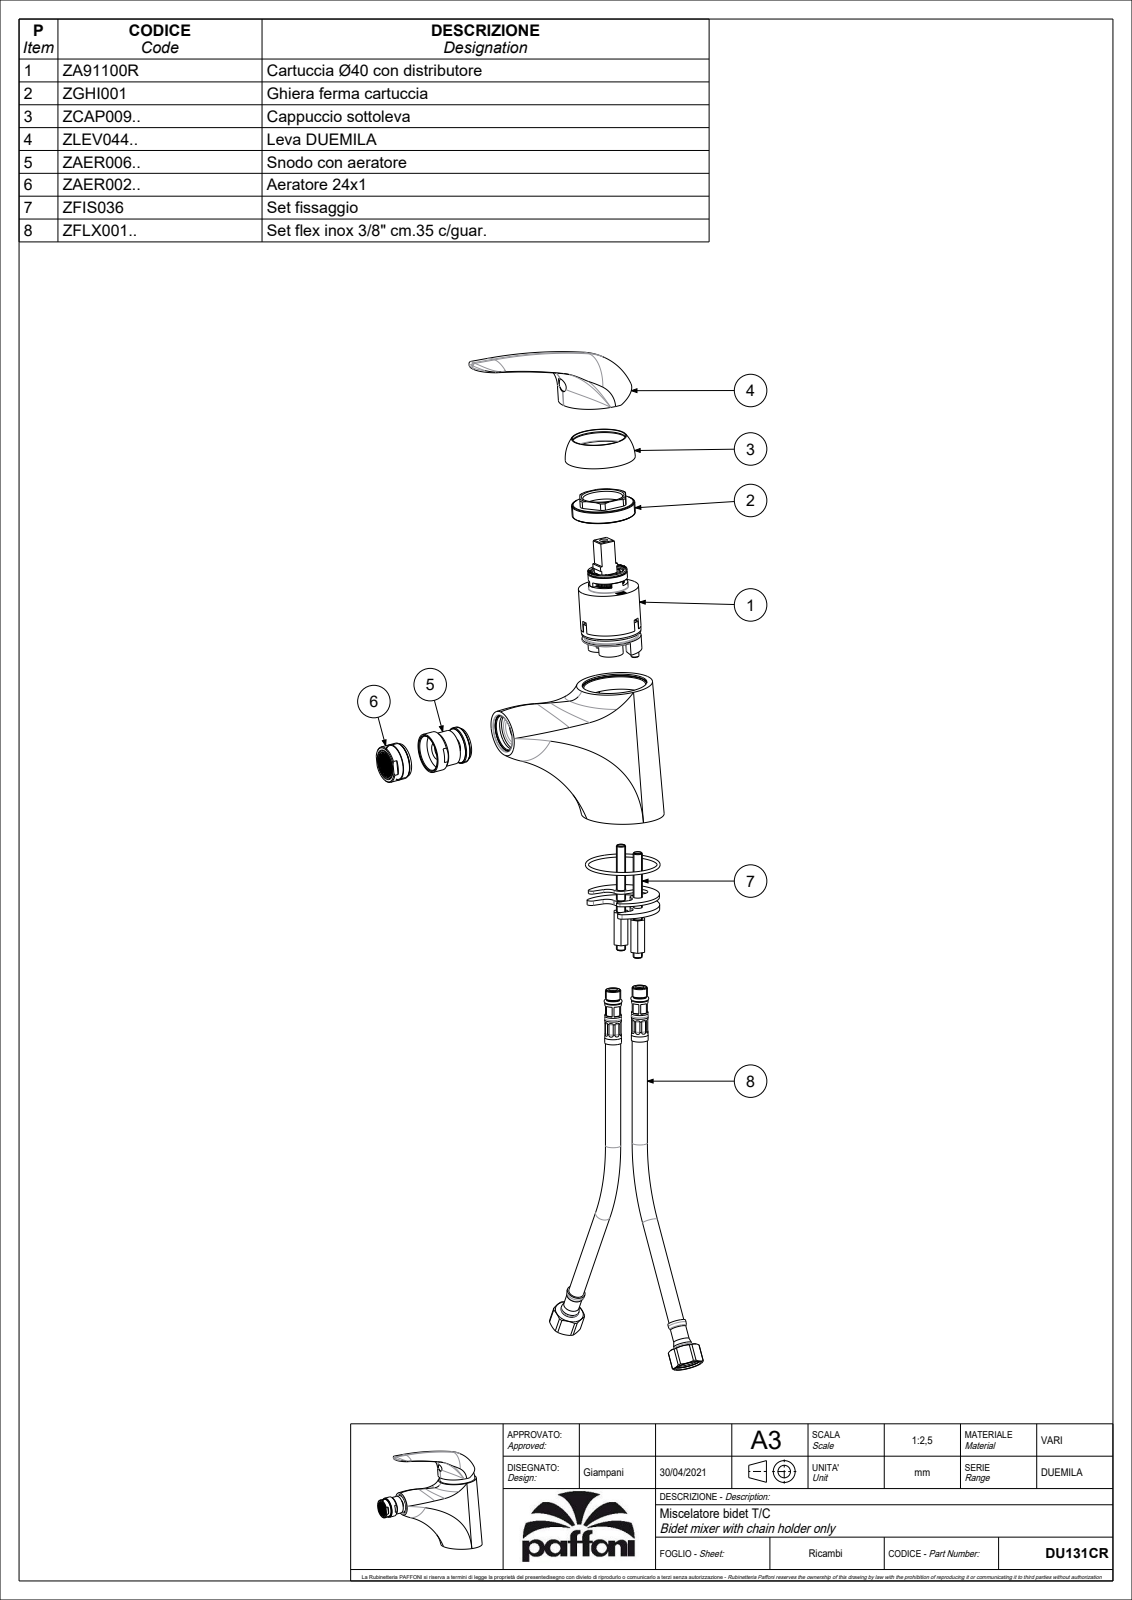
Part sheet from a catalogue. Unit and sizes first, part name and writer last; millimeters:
Units: millimetres
Overall size (bounding box): 148.69 × 132.2 × 54.3
Round holes (diameter × count): ⌀8 ×5, ⌀11 ×3, ⌀3.3 ×2, ⌀5.5 ×2, ⌀7 ×2, ⌀9 ×2, ⌀12 ×2, ⌀16 ×2, ⌀21 ×2, ⌀4 ×1, ⌀5 ×1, ⌀6 ×1
Round bosses / shafts (diameter × count): ⌀10 ×3, ⌀8 ×3, ⌀25.8 ×2, ⌀24 ×2, ⌀15.9 ×2, ⌀9.4 ×2, ⌀44.5 ×1, ⌀39.5 ×1
Partial cylindrical surfaces — rounded edges, fillets, slot ends (radius × count): R0.5 ×57, R0.2 ×28, R1.5 ×12, R7.5 ×6, R0.3 ×4, R5 ×3, R1 ×2, R5.5 ×2
Main face-to-face distances: 3.5, 13.01, 10, 1, 6.5, 5.5, 4.5, 9.51, 20, 0.5
Hole centre spacings: 8.61, 14, 2, 9.91, 13.04, 14.14, 1.3, 5.99
Volume: 190 254 mm³ · Surface area: 104 657 mm²
Bodies: 2 solids, 2723 faces (2027 planar, 399 cylindrical, 297 other)
Part name (STEP PRODUCT): DU131CR
STEP written by: CREO PARAMETRIC BY PTC INC, 2020044 (CONFIG_CONTROL_DESIGN)
